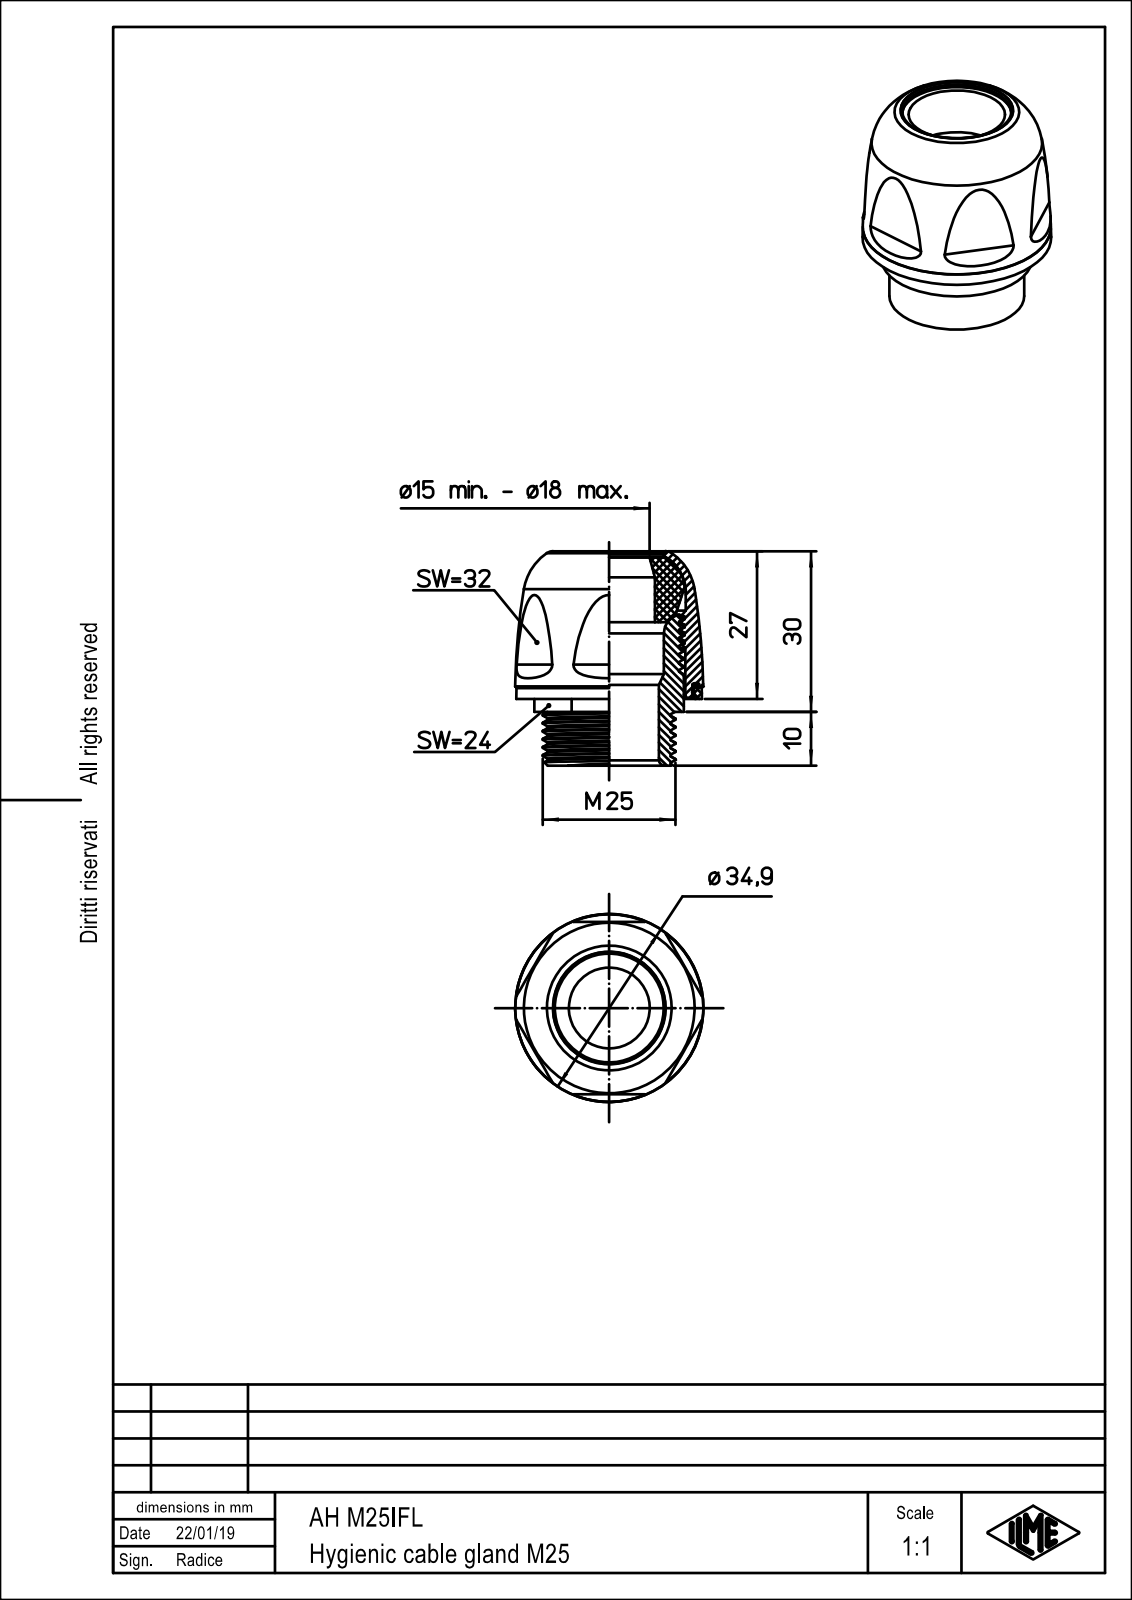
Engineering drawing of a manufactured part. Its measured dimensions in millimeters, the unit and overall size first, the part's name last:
Units: millimetres
Overall size (bounding box): 39.78 × 35 × 35
Round holes (diameter × count): ⌀17.9 ×1, ⌀18 ×1, ⌀20.2 ×1
Round bosses / shafts (diameter × count): ⌀28 ×1, ⌀25 ×1
Partial cylindrical surfaces — rounded edges, fillets, slot ends (radius × count): R3 ×6
Main face-to-face distances: 32, 12.5, 8, 4.5, 38.9, 30.9, 26.4, 39.79, 31.79, 27.29
Volume: 18 720 mm³ · Surface area: 7 053 mm²
Bodies: 1 solid, 43 faces (13 planar, 16 cylindrical, 14 other)
Part name (STEP PRODUCT): AH_M25IFL
STEP written by: PTC Creo Elements/Direct Modeling 19.0E 27-Jun-2016 (C) Parametric Technology GmbH (AUTOMOTIVE_DESIGN)
